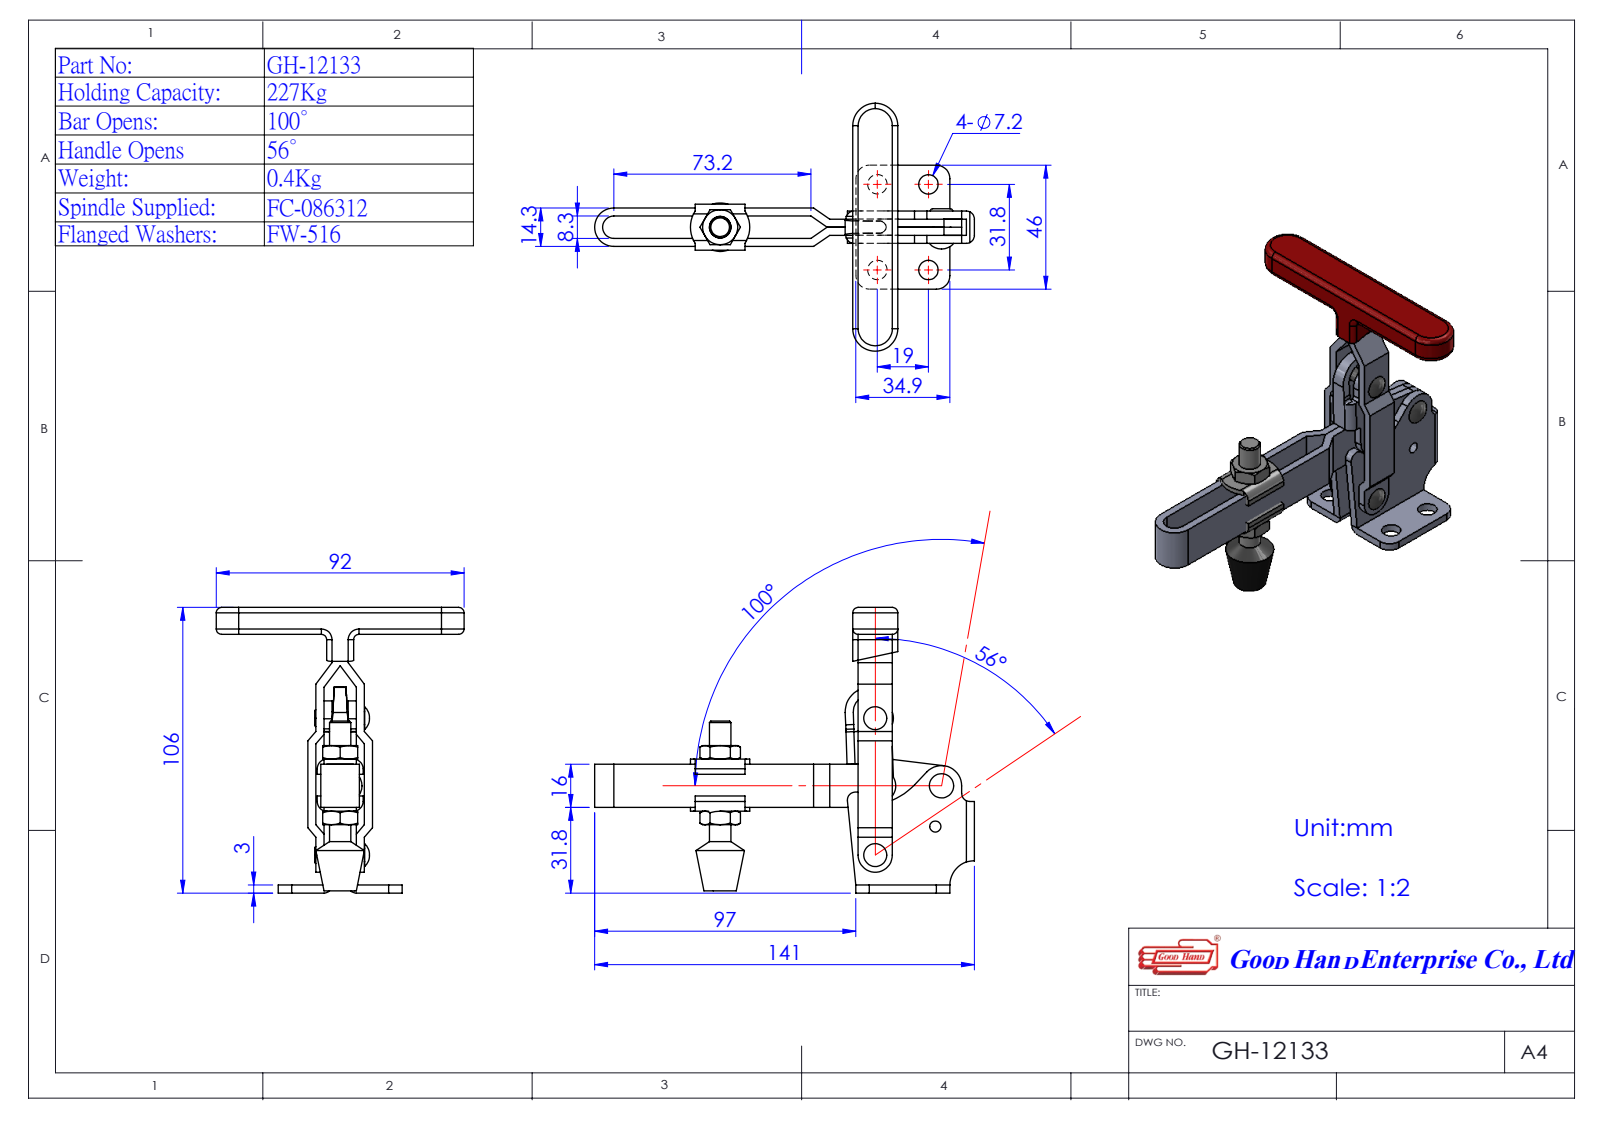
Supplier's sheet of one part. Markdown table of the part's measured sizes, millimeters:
| quantity | value |
| --- | --- |
| part name | Group4^GH-12133(簡化); Group2^GH-12133(簡化); Group5^GH-12133(簡化); GH-12133(簡化) (+2 more) |
| STEP written by | SolidWorks 2016 (AUTOMOTIVE_DESIGN) |
| units | millimeters |
| bodies | 5 solids, 295 faces (151 planar, 91 cylindrical, 53 other) |
| overall size | 141 × 106 × 92 |
| volume | 61 654 mm³ |
| surface area | 38 143 mm² |
| round holes (diameter × count) | 4 × 4, 7.2 × 4 |
| round bosses / shafts (diameter × count) | 6.3 × 2, 7.93 × 1 |
| partial cylindrical surfaces (radius × count) | 1.5 × 4, 3 × 4, 5 × 4, 7.5 × 4, 1 × 2, 6.4 × 2, 8.35 × 2, 9 × 2 |
| main face-to-face distances | 3, 1.15, 10.15, 9, 6, 4.15, 13.15, 11.3, 1.85, 7.15 |
| hole center spacings | 19, 31.8, 37.04, 23.4, 25.13, 25.73, 35.14, 35.58 |
